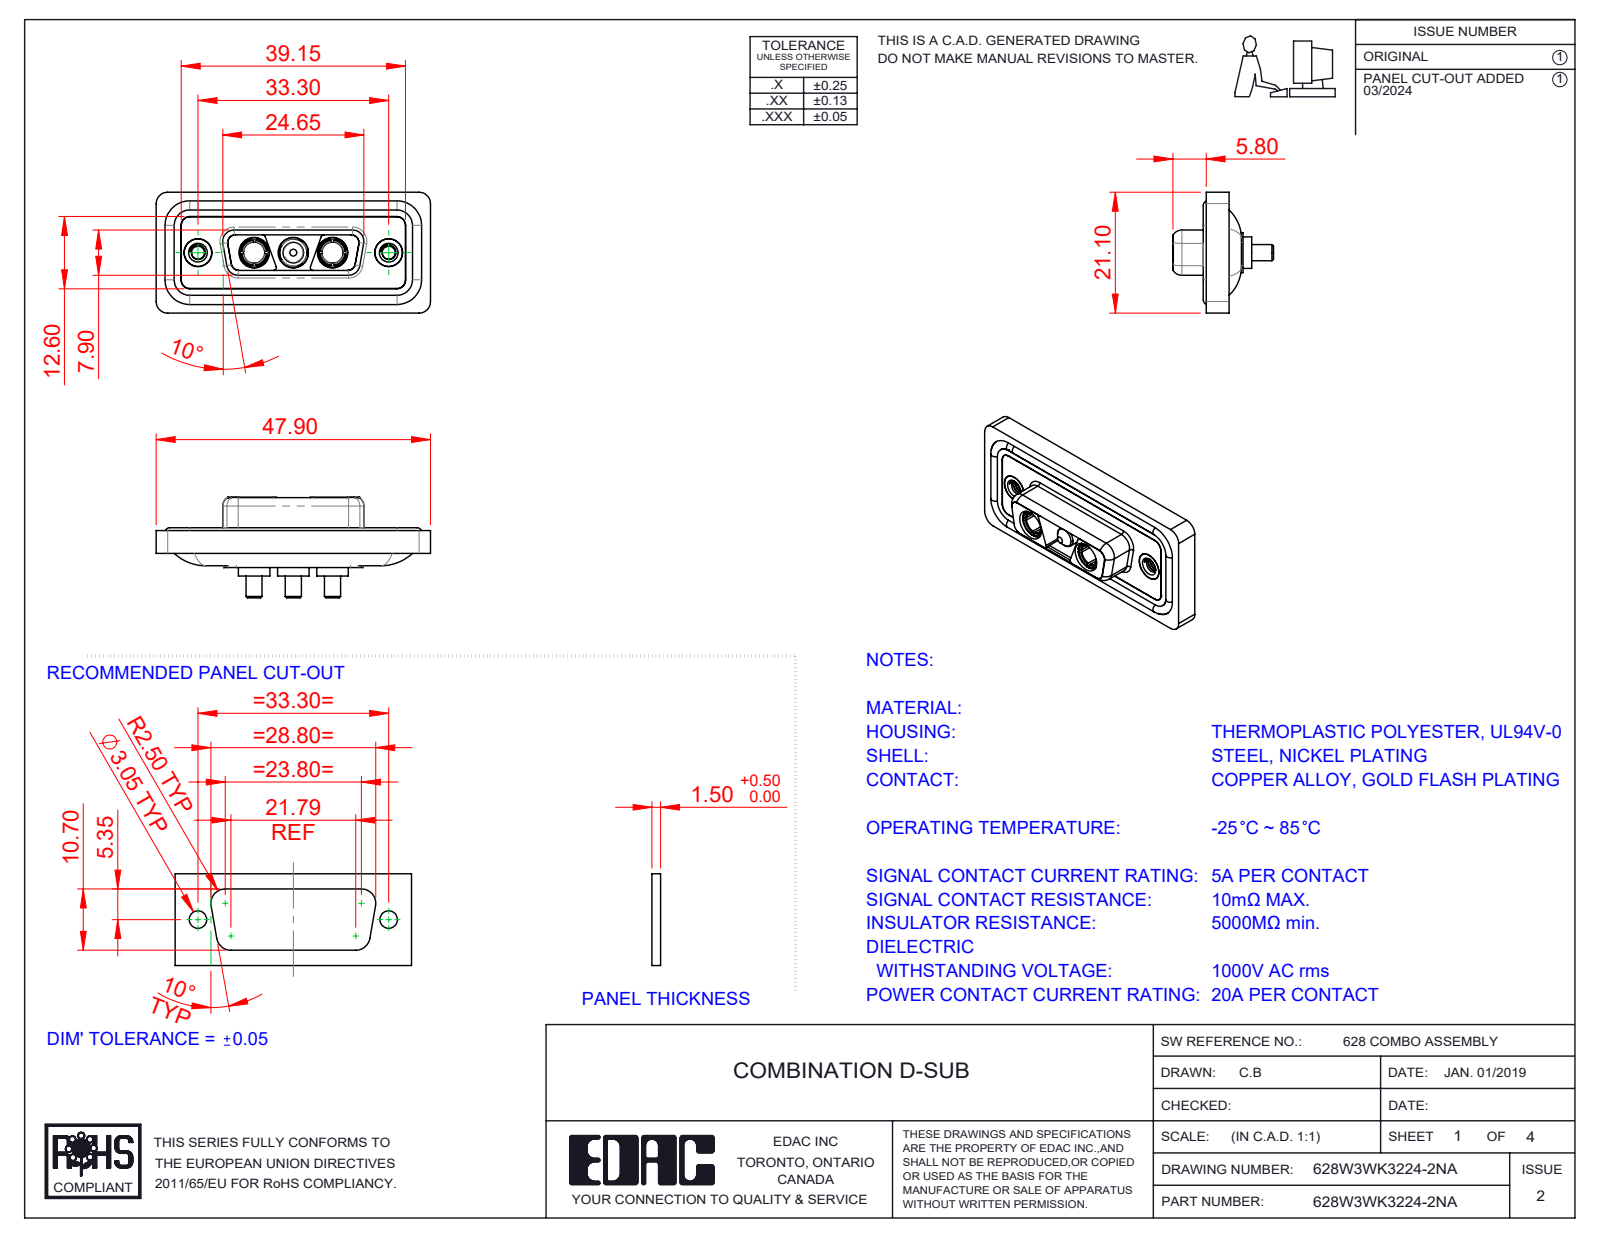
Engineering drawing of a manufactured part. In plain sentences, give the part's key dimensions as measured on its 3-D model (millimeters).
The part is named "628Combo Shell Front_15 Contacts; 628Combo Shell Rear_15 Contacts; 628W3WK3224-2NA; 628Combo Threaded Rivet_A (+4 more)". Its 3-D file was written by "SolidWorks 2023 (CONFIG_CONTROL_DESIGN)". It is 13 solids with 581 faces: 178 planar, 260 cylindrical and 143 other. Overall it measures 47.9 by 21.1 by 17.55 millimeters. Its volume is 5 880 cubic millimeters and its surface area 9 502 square millimeters. Round holes: 5 of diameter 4.85, 3 of diameter 5.3, 2 of diameter 2.26, 2 of diameter 3.7, 2 of diameter 4, 2 of diameter 4.05, 2 of diameter 5. Round bosses or shafts: 4 of diameter 1.6, 3 of diameter 5.5, 3 of diameter 5.2, 3 of diameter 4.75, 3 of diameter 3.75, 3 of diameter 2.8, 2 of diameter 4.96, 2 of diameter 4.95. Partial cylindrical surfaces (rounded edges, fillets, slot ends): 22 of radius 1.5, 20 of radius 2, 12 of radius 1.35, 8 of radius 0.5, 8 of radius 1.6, 4 of radius 0.25, 4 of radius 0.6, 4 of radius 0.65. The main face-to-face distances are 0.4, 1.6, 1.8, 0.5, 1.1, 2.9, 5.65, 7.05, 1.5, 5.35. The hole center spacings are 6.85, 9.8, 16.65, 23.5, 13.7, 33.3.
